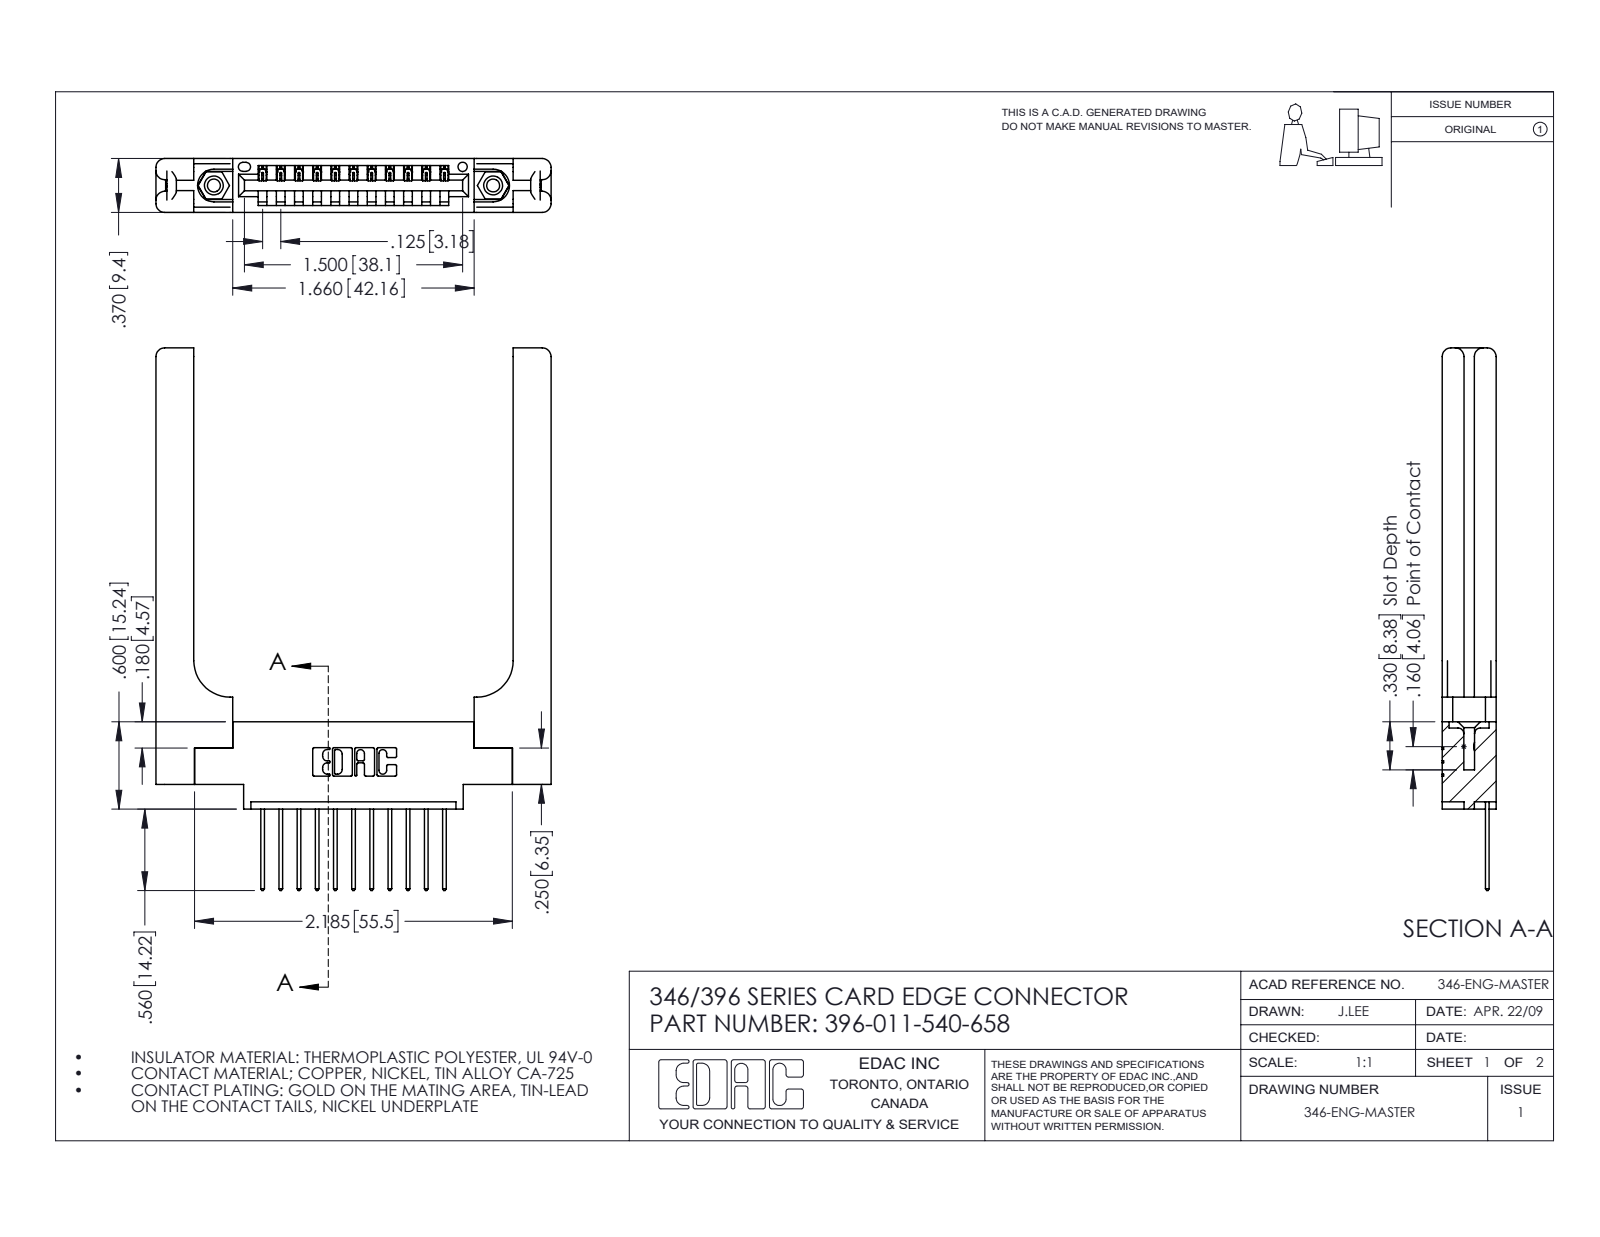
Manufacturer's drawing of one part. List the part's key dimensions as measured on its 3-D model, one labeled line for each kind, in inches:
Part name (STEP PRODUCT): 346 Part_0.170 Offset - 0.156 Dia-TH; 346-220-058_345-220-058; 345-292-001_345-293-140; 396-011-540-658 (+1 more)
STEP written by: SolidWorks 2016 (CONFIG_CONTROL_DESIGN)
Units: inches
Bodies: 16 solids, 1020 faces (668 planar, 292 cylindrical, 60 other)
Overall size (bounding box): 3.73 × 2.716 × 0.37
Volume: 0.84 in³ · Surface area: 20.02 in²
Round holes (diameter × count): ⌀0.089 ×2, ⌀0.125 ×2, ⌀0.156 ×2, ⌀0.064 ×1
Round bosses / shafts (diameter × count): ⌀0.155 ×2
Partial cylindrical surfaces — rounded edges, fillets, slot ends (radius × count): R0.006 ×22, R0.01 ×22, R0.01 ×22, R0.06 ×16, R0.007 ×6, R0.031 ×6, R0.026 ×3, R0.03 ×2
Main face-to-face distances: 0.37, 0.15, 0.072, 0.148, 0.22, 0.048, 0.322, 0.102, 0.25, 0.173
Hole centre spacings: 0.246, 1.715, 1.92
